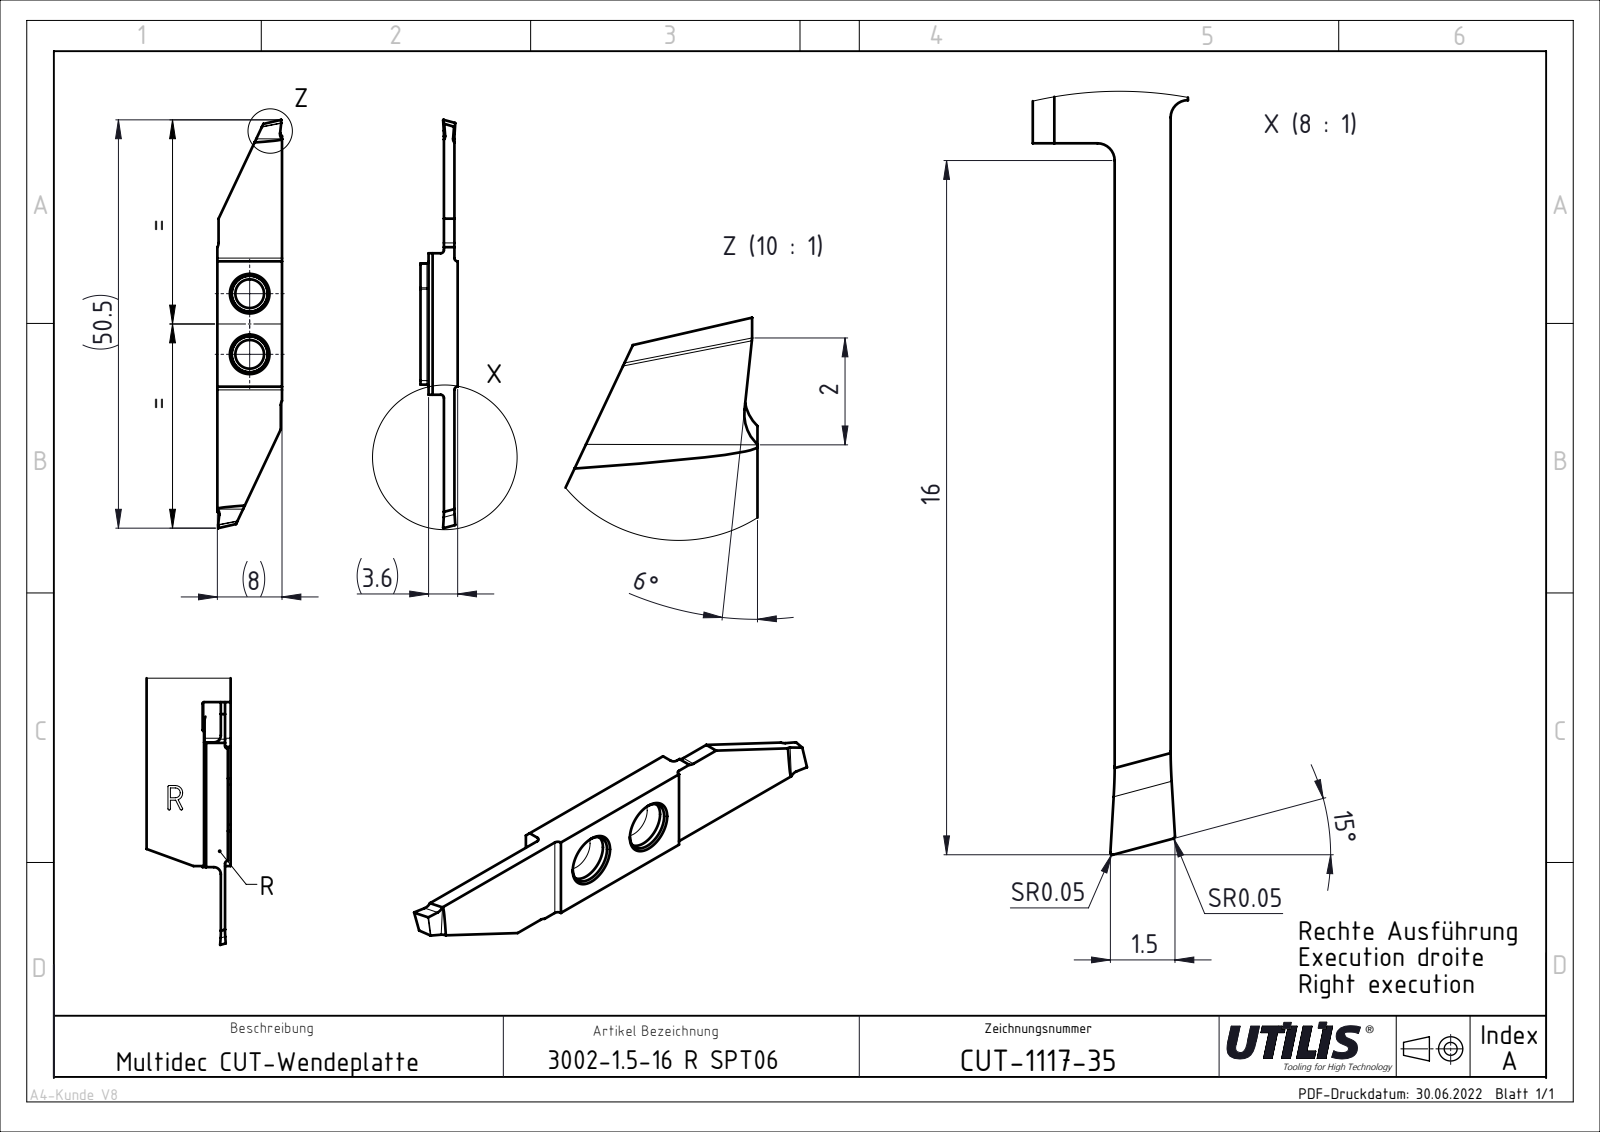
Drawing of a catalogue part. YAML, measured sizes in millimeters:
part_name: "CUT-1117; ASME Y14.5"
step_written_by: "FormatWorks Professional (AP242_MANAGED_MODEL_BASED_3D_ENGINEERING_MIM_LF)"
units: millimeters
bodies: {solids: 1, faces: 40, planar: 24, cylindrical: 16, other: 0}
overall_size: [50.5, 8, 3.6]
volume: 668
surface_area: 937
round_holes:
  - {diameter: 3.55, count: 2}
partial_cylinders:
  - {radius: 0.4, count: 4}
  - {radius: 1, count: 2}
face_to_face_distances: [1.3, 1.7, 0.4, 1.9, 3.2, 3.6, 8, 18.09, 17.5, 7.85]
hole_center_spacings: [7.5]
